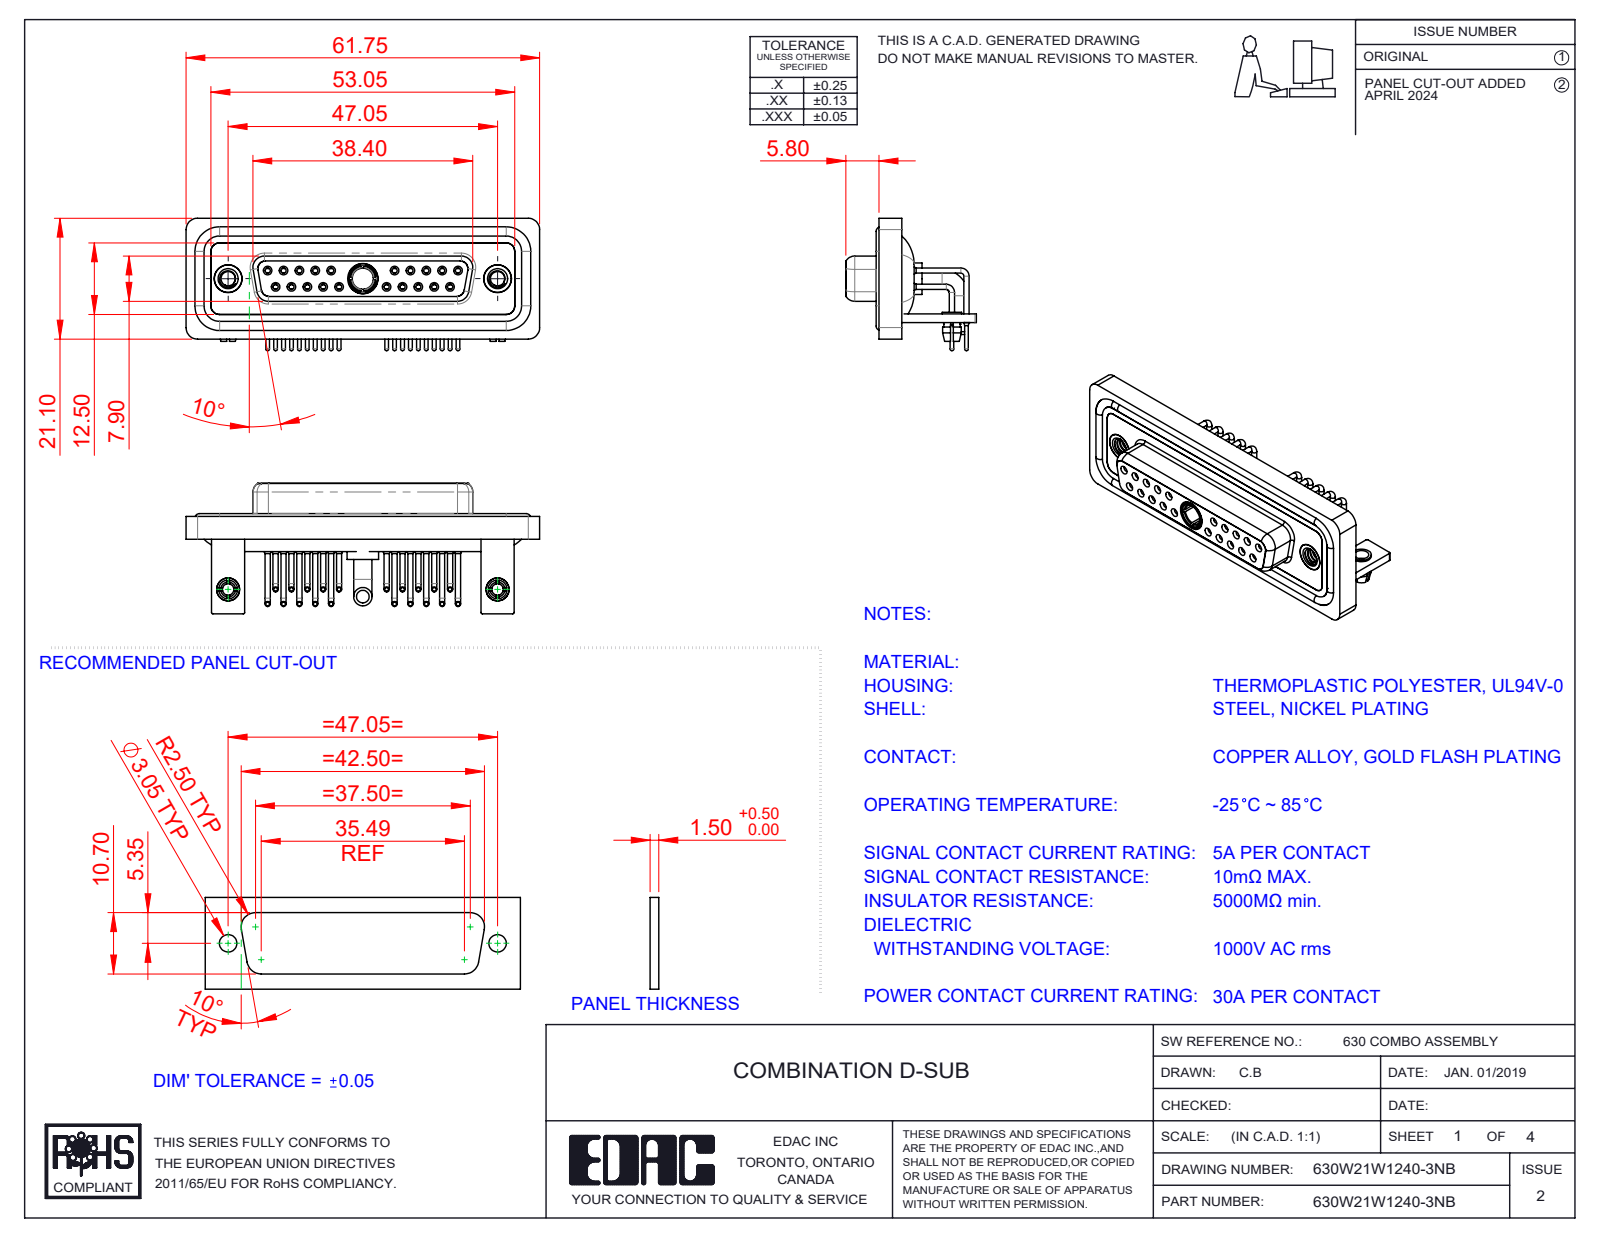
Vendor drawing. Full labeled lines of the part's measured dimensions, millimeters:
Part name (STEP PRODUCT): 630W21W1240-3NB; Power Socket_30A RA; 630Combo Contact Row 1_50 Contacts; 630Combo Board Lock_50 Contacts (+7 more)
STEP written by: SolidWorks 2023 (CONFIG_CONTROL_DESIGN)
Units: millimetres
Bodies: 33 solids, 1658 faces (502 planar, 727 cylindrical, 429 other)
Overall size (bounding box): 61.75 × 23.12 × 22.8
Volume: 8 929 mm³ · Surface area: 15 747 mm²
Round holes (diameter × count): ⌀2 ×22, ⌀0.9 ×20, ⌀1.1 ×20, ⌀1.5 ×20, ⌀1.6 ×10, ⌀1.7 ×10, ⌀2.5 ×4, ⌀4.85 ×3, ⌀3.2 ×2, ⌀4 ×2, ⌀4.05 ×2, ⌀5 ×2
Round bosses / shafts (diameter × count): ⌀0.9 ×20, ⌀0.65 ×20, ⌀1.6 ×14, ⌀4.95 ×2, ⌀4.8 ×2, ⌀4 ×2, ⌀3.4 ×2, ⌀3.3 ×2
Partial cylindrical surfaces — rounded edges, fillets, slot ends (radius × count): R2 ×19, R1.5 ×18, R0.25 ×16, R1.35 ×8, R1.6 ×8, R0.5 ×5, R0.6 ×4, R0.65 ×4
Main face-to-face distances: 0.4, 1.8, 2.9, 3.7, 1.5, 4.1, 1.1, 1.4, 1.6, 2.5
Hole centre spacings: 3.16, 2.77, 5.54, 8.31, 5.04, 19.39, 20.97, 22.16
